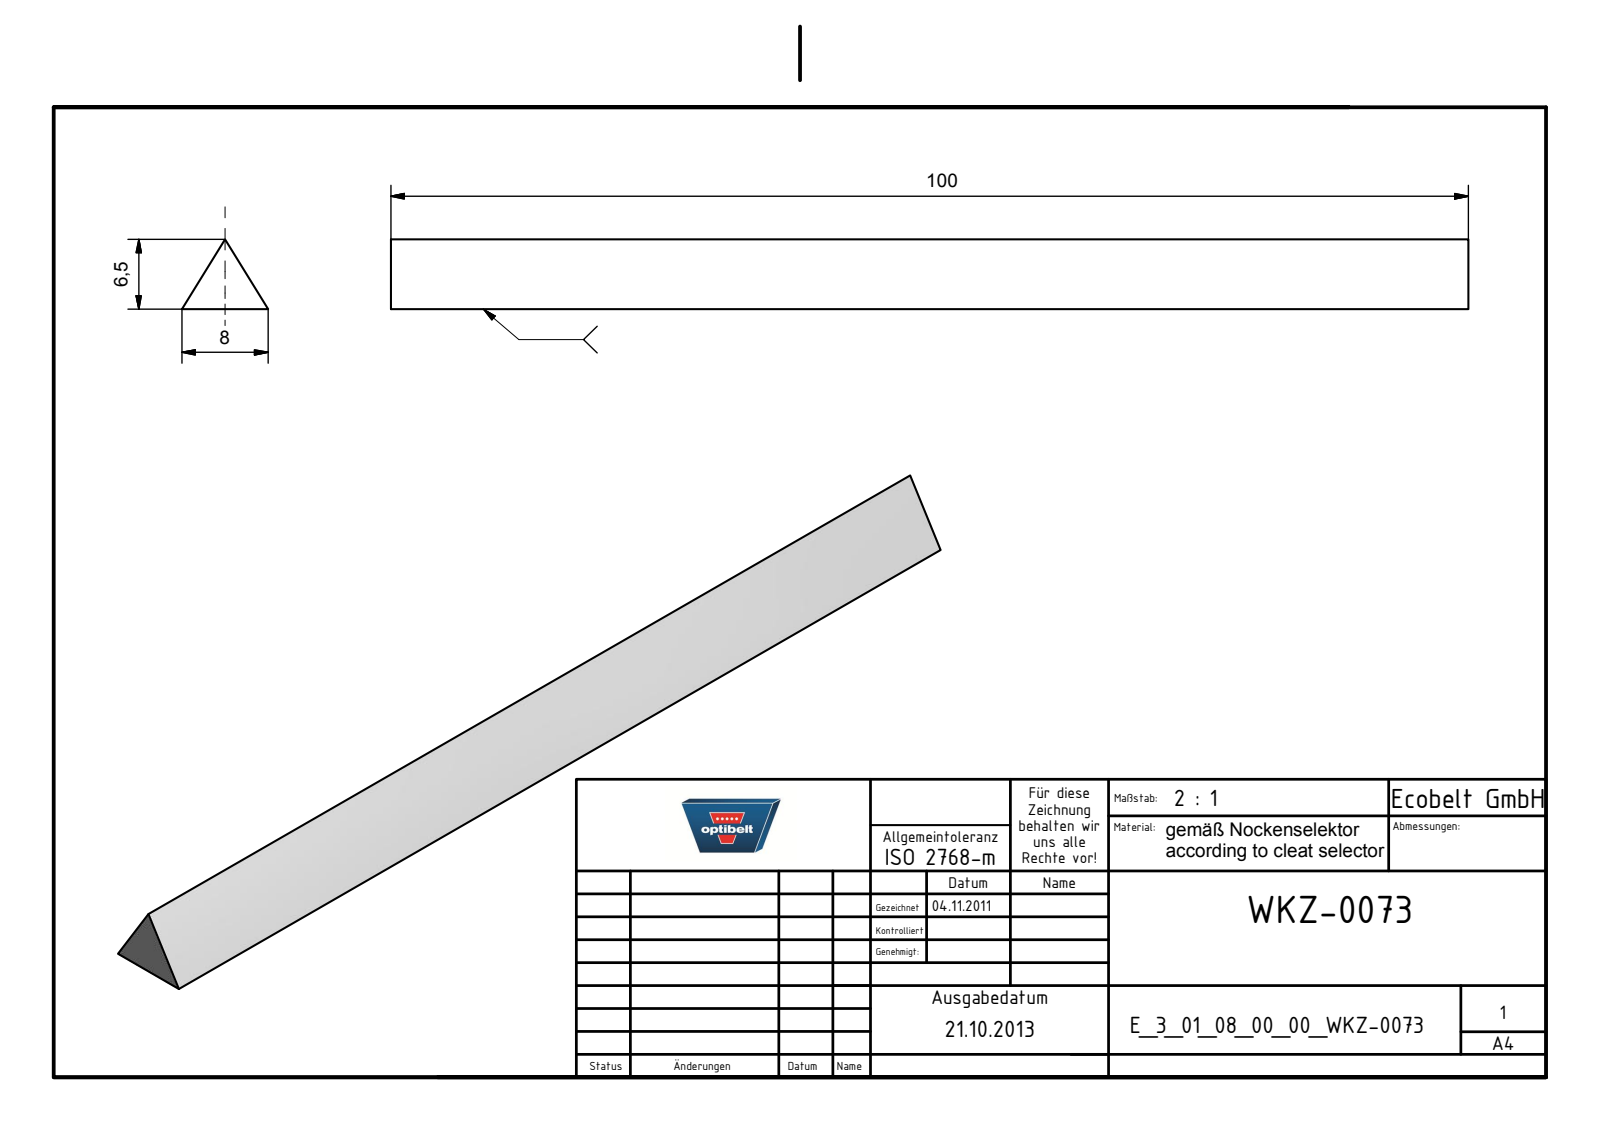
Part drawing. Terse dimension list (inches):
name: E_3_01_08_00_00_WKZ-0073
written by: Autodesk Inventor 2025 (AUTOMOTIVE_DESIGN)
unit: in
bodies: 1 solid, 5 faces (5 planar, 0 cylindrical, 0 other)
size: 3.937 × 0.315 × 0.256
volume: 0.159 in³; area: 3.686 in²
face distances: 3.937
